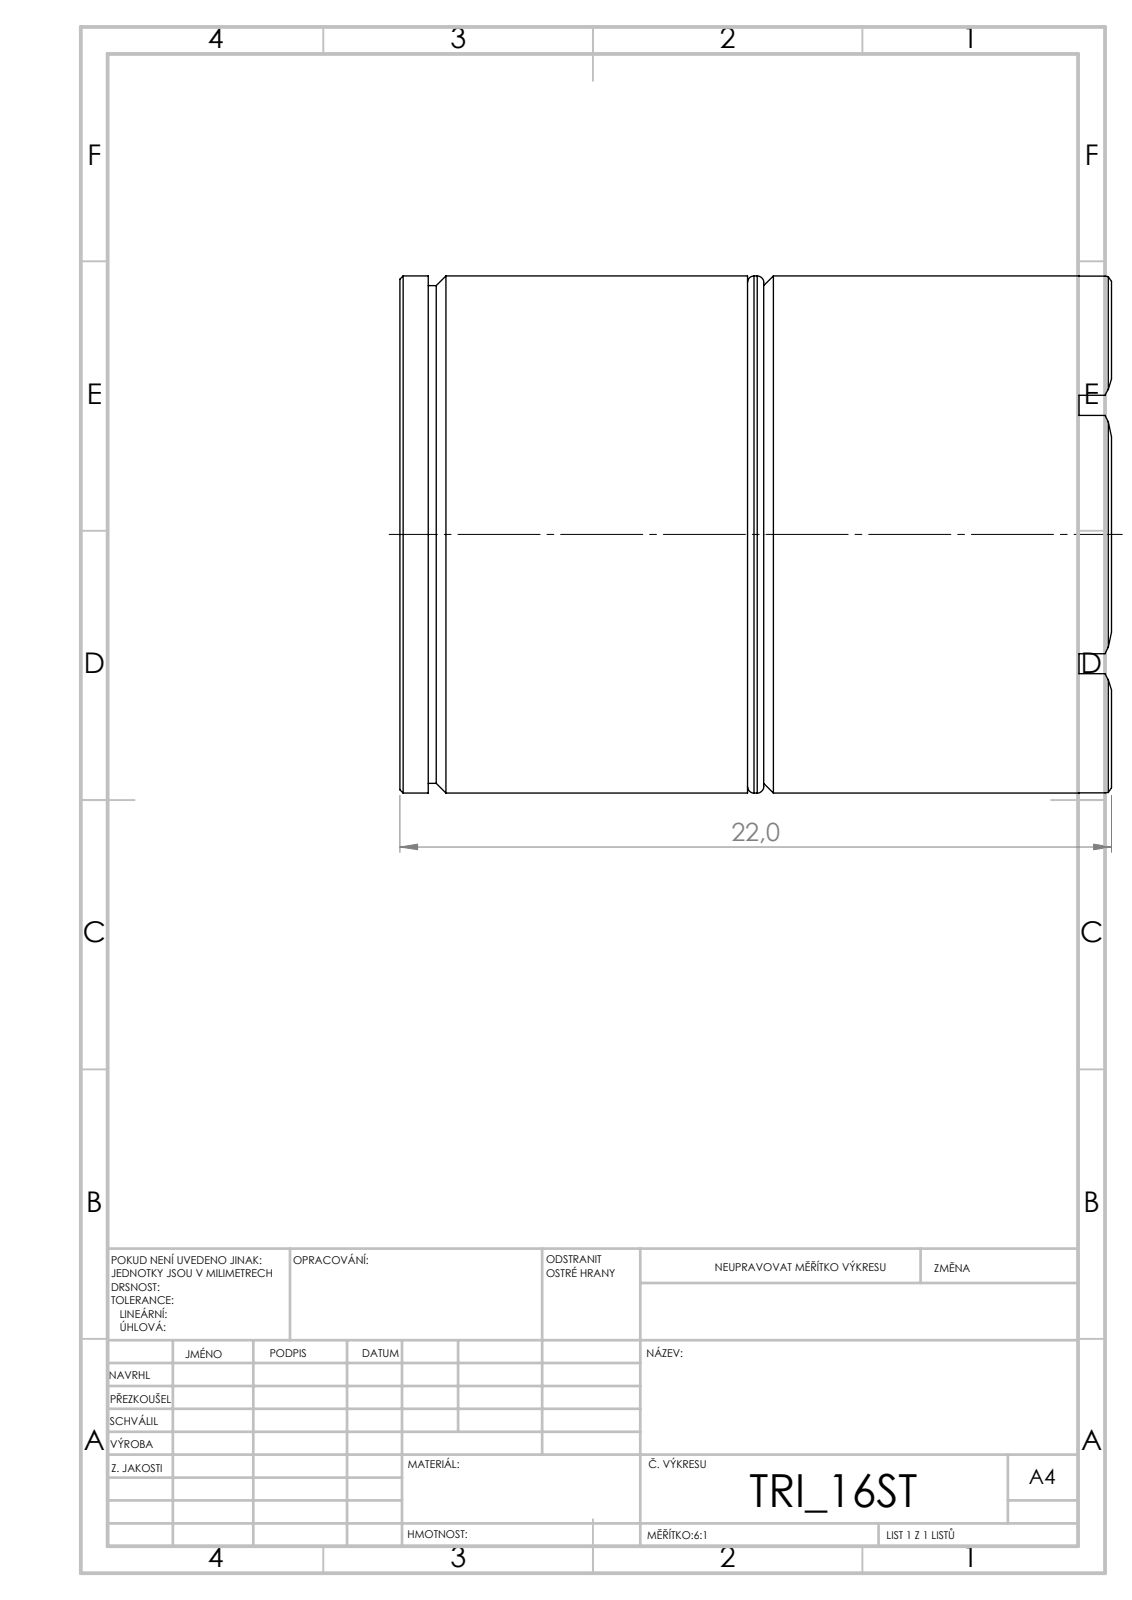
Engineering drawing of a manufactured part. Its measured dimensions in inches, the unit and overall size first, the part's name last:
Units: inches
Overall size (bounding box): 0.866 × 0.63 × 0.63
Round bosses / shafts (diameter × count): ⌀0.63 ×1, ⌀0.606 ×1
Main face-to-face distances: 0.423, 0.443, 0.02, 0.384, 0.404, 0.827, 0.559, 0.793, 0.409, 0.389
Volume: 0.264 in³ · Surface area: 3.092 in²
Bodies: 2 solids, 53 faces (24 planar, 12 cylindrical, 17 other)
STEP written by: SolidWorks 2019 (CONFIG_CONTROL_DESIGN)
